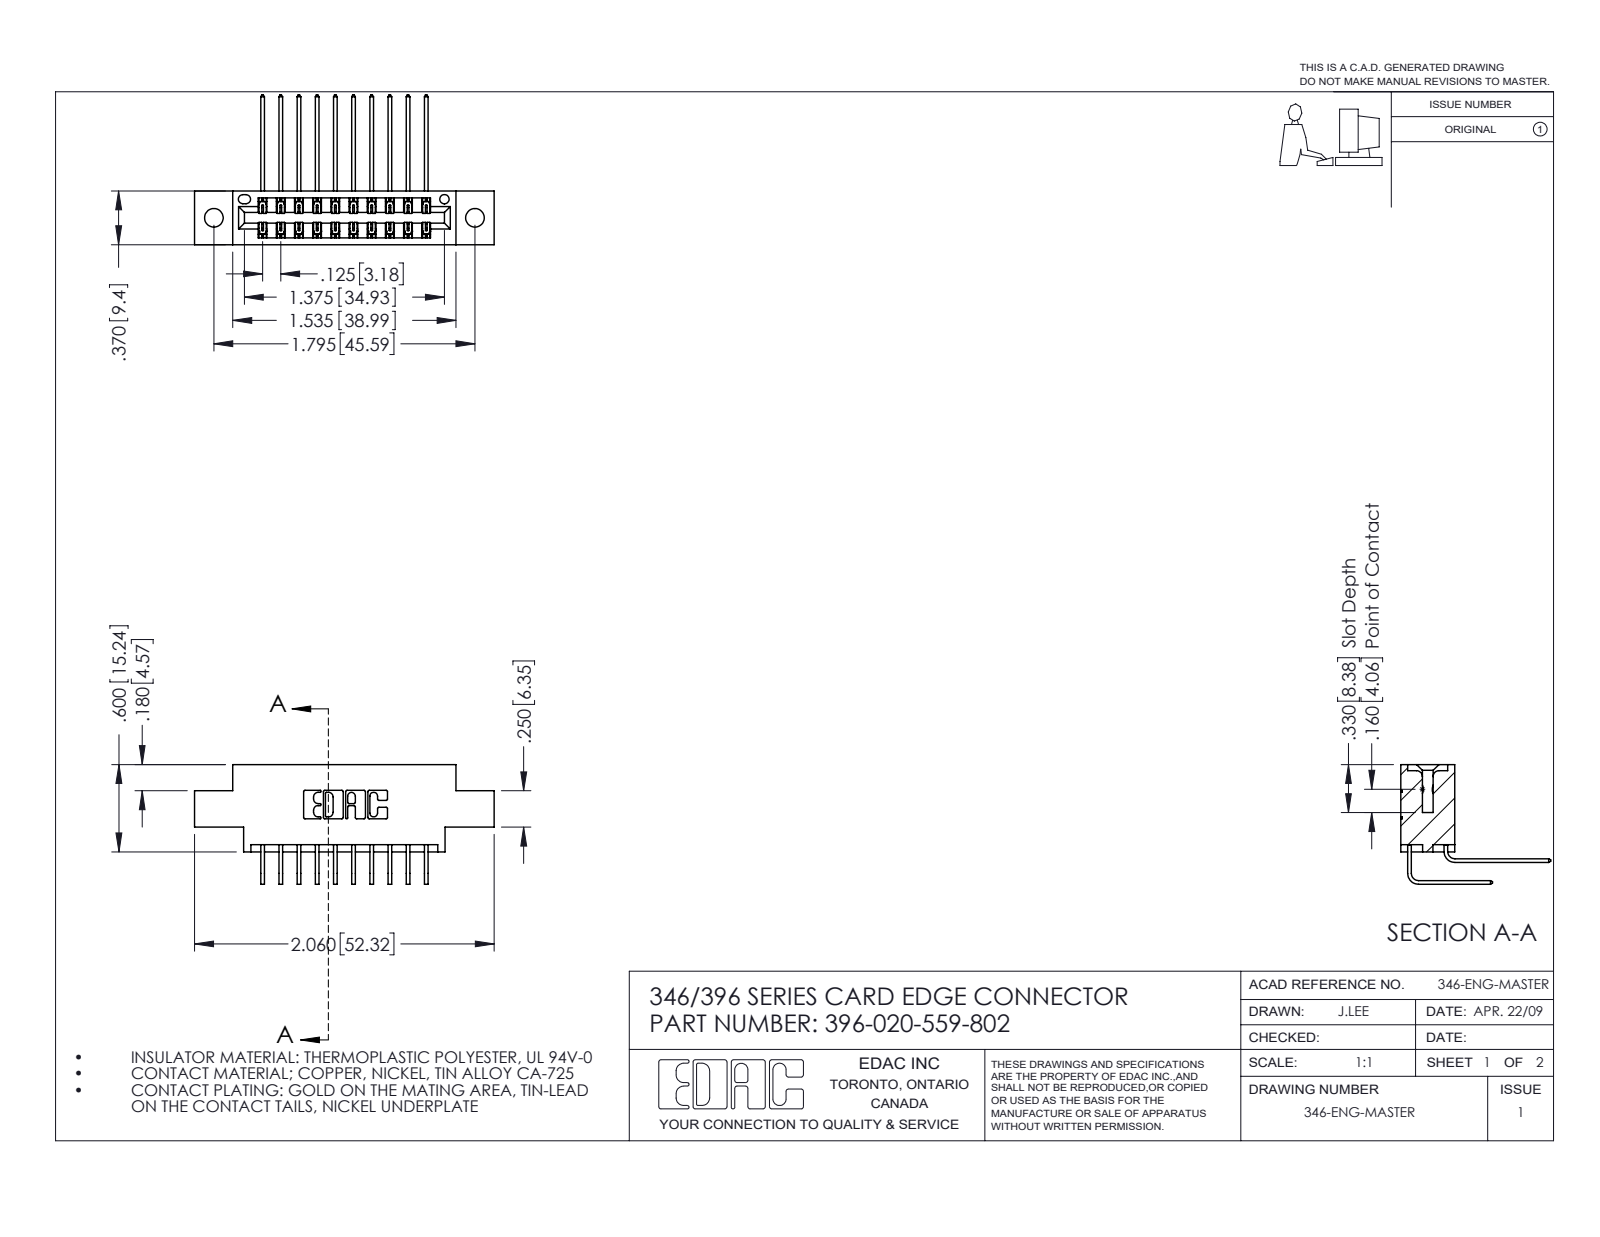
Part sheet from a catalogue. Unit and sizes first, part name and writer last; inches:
Units: inches
Overall size (bounding box): 2.06 × 1.03 × 0.823
Round holes (diameter × count): ⌀0.128 ×2, ⌀0.064 ×1
Partial cylindrical surfaces — rounded edges, fillets, slot ends (radius × count): R0.006 ×30, R0.01 ×22, R0.007 ×6, R0.031 ×6, R0.026 ×3, R0.014 ×2, R0.022 ×2, R0.024 ×2
Main face-to-face distances: 0.25, 0.048, 0.37, 0.322, 0.025, 0.072, 0.298, 0.275, 0.148, 0.222
Hole centre spacings: 0.246, 1.59, 1.795
Volume: 0.292 in³ · Surface area: 10.12 in²
Bodies: 21 solids, 1206 faces (820 planar, 386 cylindrical, 0 other)
Part name (STEP PRODUCT): 345-292-001_558 559 Tail - 1; 345-292-001_559 Tail - 2; 396-020-559-802; 346 Part_0.170 Offset - 0.128 Dia
STEP written by: SolidWorks 2016 (CONFIG_CONTROL_DESIGN)
